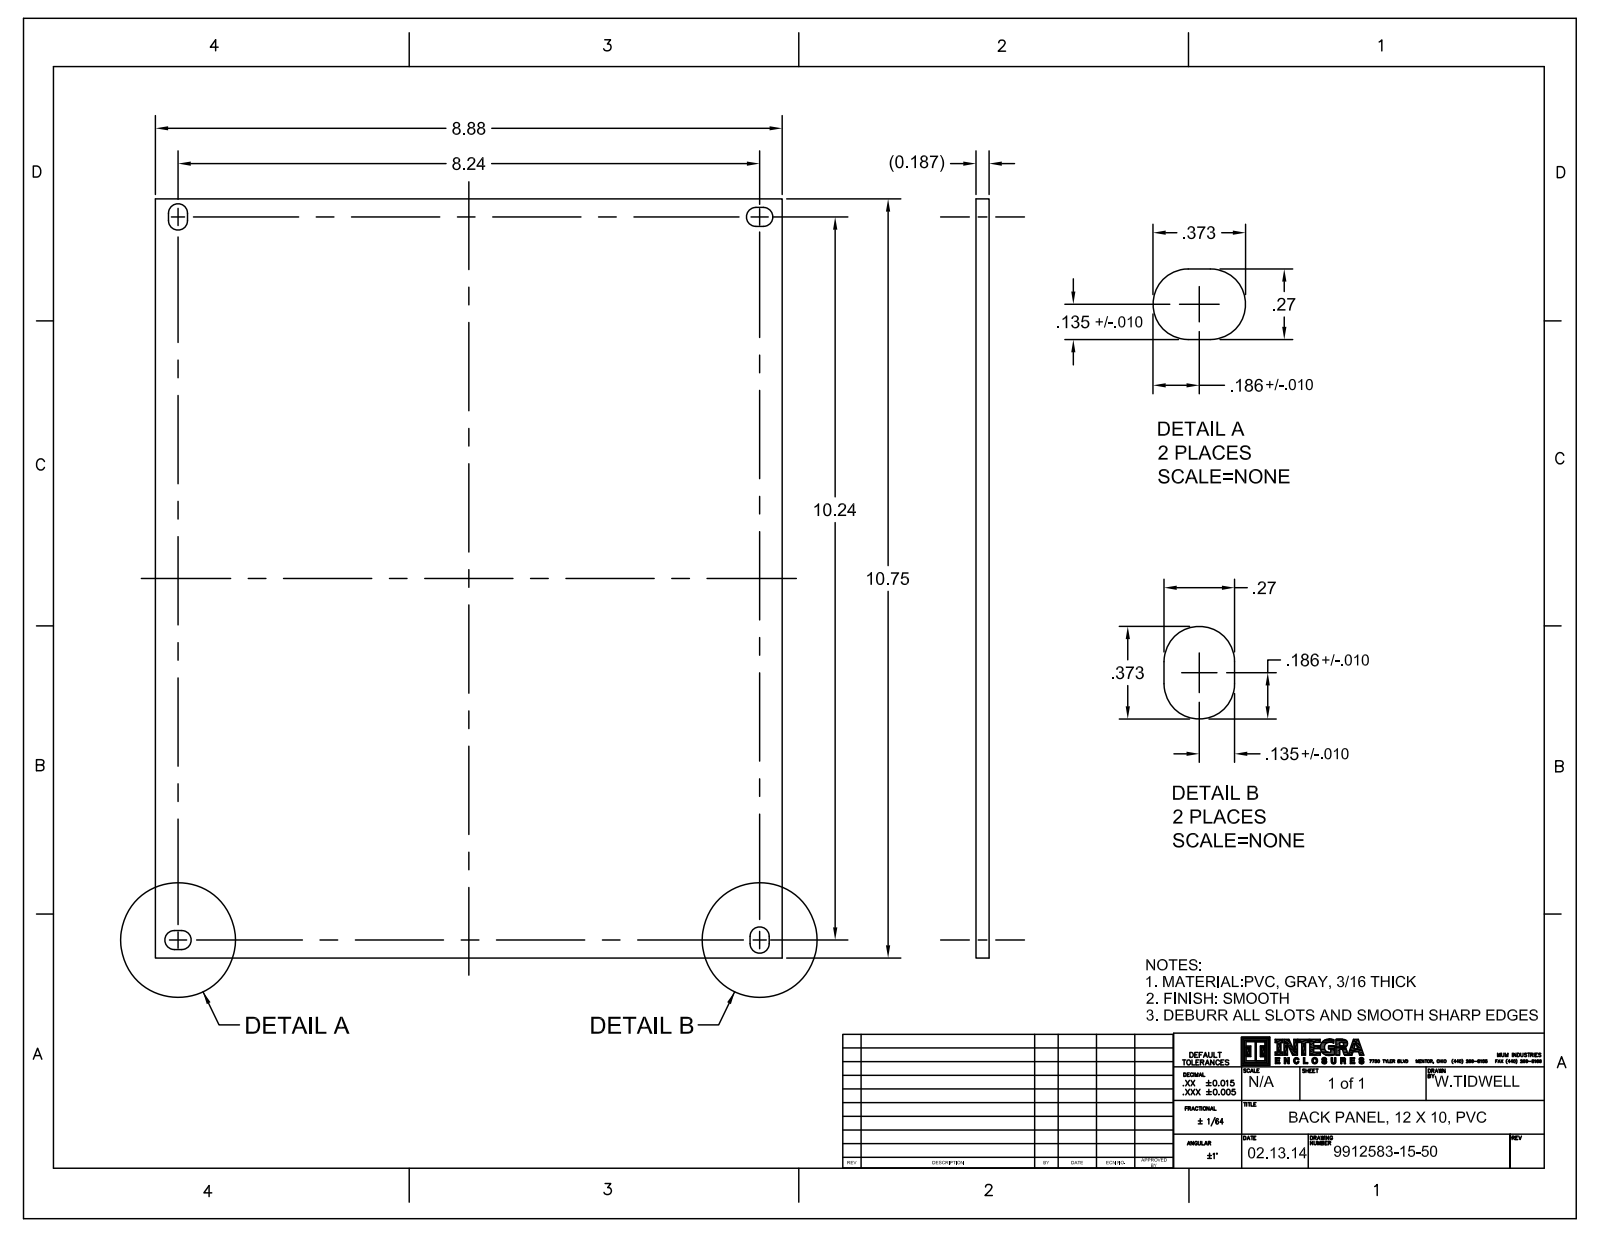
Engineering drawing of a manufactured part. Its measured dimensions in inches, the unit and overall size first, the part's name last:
Units: inches
Overall size (bounding box): 10.75 × 8.88 × 0.63
Round bosses / shafts (diameter × count): ⌀0.373 ×4, ⌀0.19 ×4, ⌀0.149 ×4
Partial cylindrical surfaces — rounded edges, fillets, slot ends (radius × count): R0.125 ×8
Main face-to-face distances: 0.187, 8.88, 10.75, 0.25, 0.313, 0.5, 0.13, 0.38, 10.37, 10.62
Volume: 17.92 in³ · Surface area: 201.6 in²
Bodies: 5 solids, 514 faces (90 planar, 336 cylindrical, 88 other)
Part name (STEP PRODUCT): 9912583-15-50; 9912537-82-10; PVCBP1210_ASM
STEP written by: CREO PARAMETRIC BY PTC INC, 2016050 (CONFIG_CONTROL_DESIGN)
